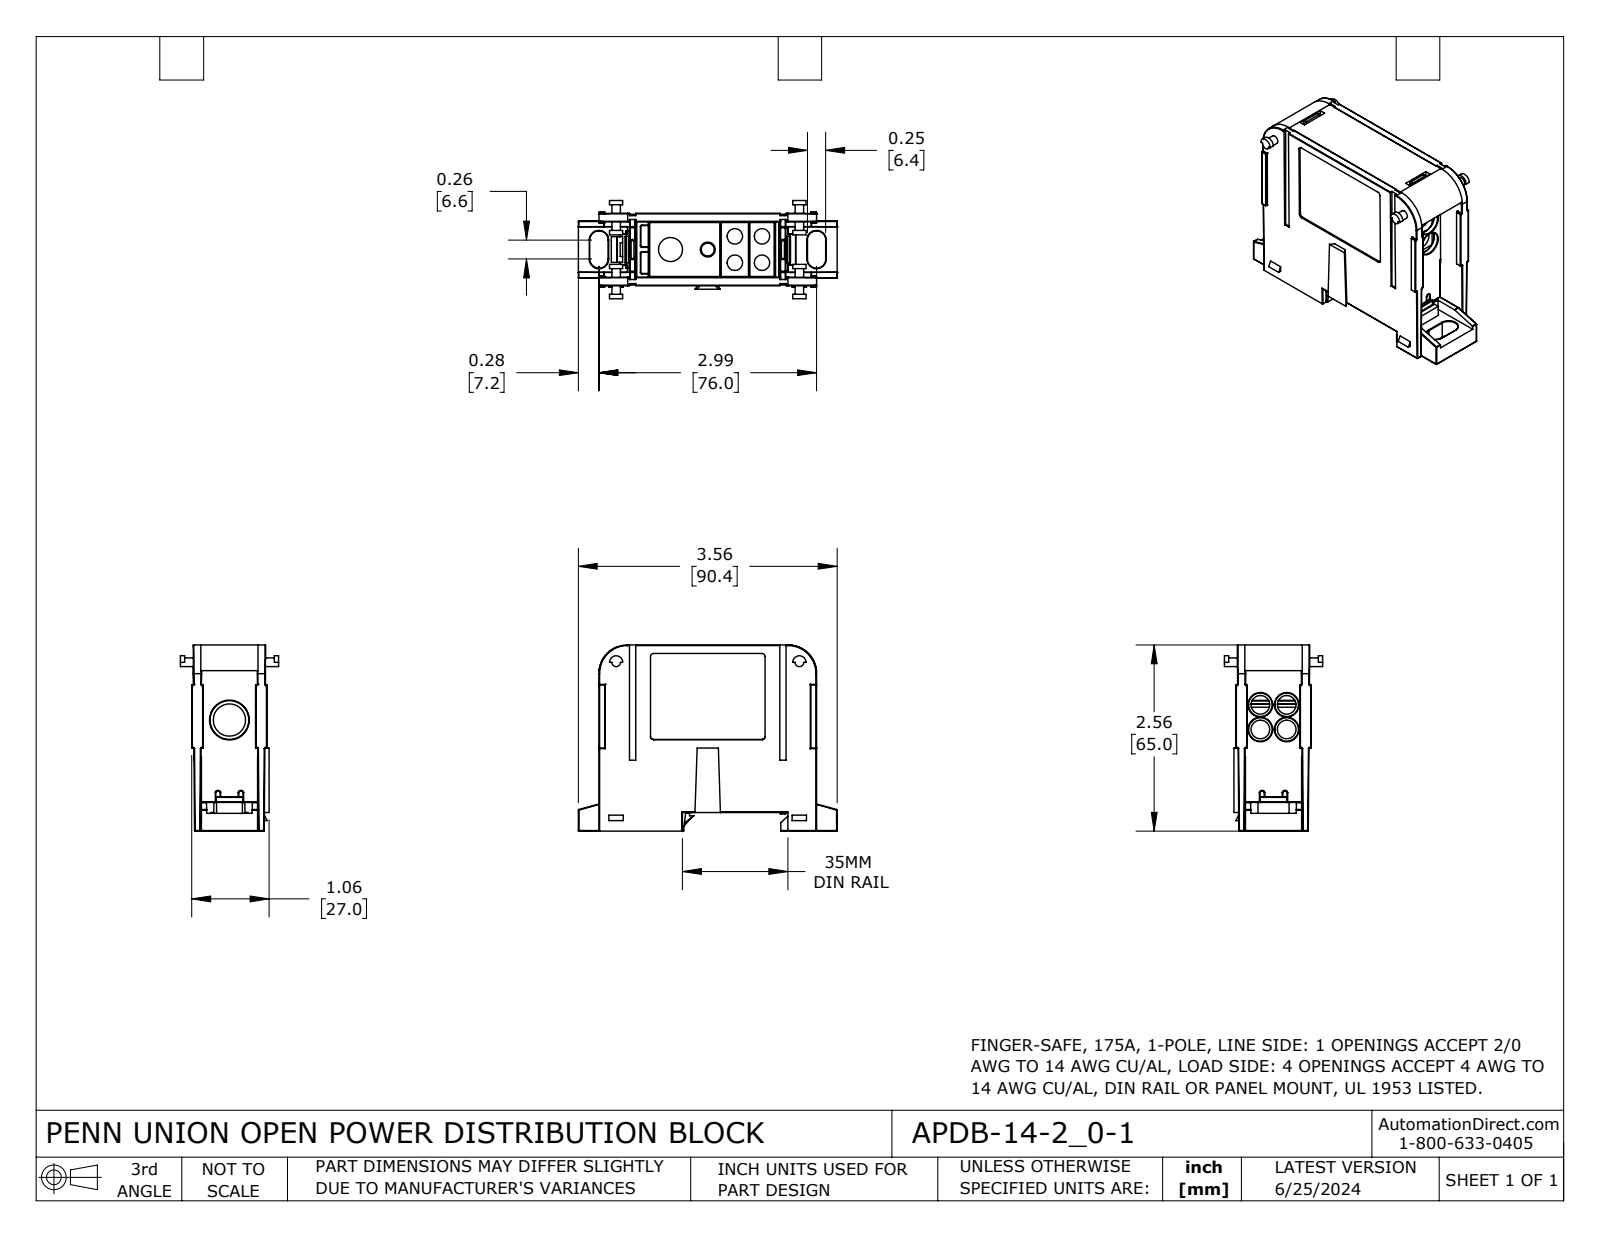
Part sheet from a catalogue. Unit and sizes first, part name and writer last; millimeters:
Units: millimetres
Overall size (bounding box): 90.4 × 65 × 34.3
Round holes (diameter × count): ⌀5.4 ×4, ⌀6.5 ×4, ⌀8.2 ×4, ⌀4.5 ×1, ⌀5.2 ×1, ⌀8.4 ×1, ⌀11.3 ×1, ⌀13.5 ×1
Round bosses / shafts (diameter × count): ⌀3 ×2
Partial cylindrical surfaces — rounded edges, fillets, slot ends (radius × count): R0.2 ×206, R0.1 ×63, R0.5 ×16, R1 ×16, R0.3 ×7, R1.1 ×4, R1.6 ×4, R3.2 ×4
Main face-to-face distances: 22.3, 2, 22.3, 52.5, 20, 19.4, 0.6, 0.5, 22.8, 34.5
Hole centre spacings: 9.2, 5.7, 7, 8.6, 9.5, 10.5, 12.6, 13.2
Volume: 55 500 mm³ · Surface area: 57 180 mm²
Bodies: 8 solids, 1390 faces (571 planar, 543 cylindrical, 276 other)
Part name (STEP PRODUCT): APDB-14-2_0-1
STEP written by: SolidWorks 2023 (CONFIG_CONTROL_DESIGN)
